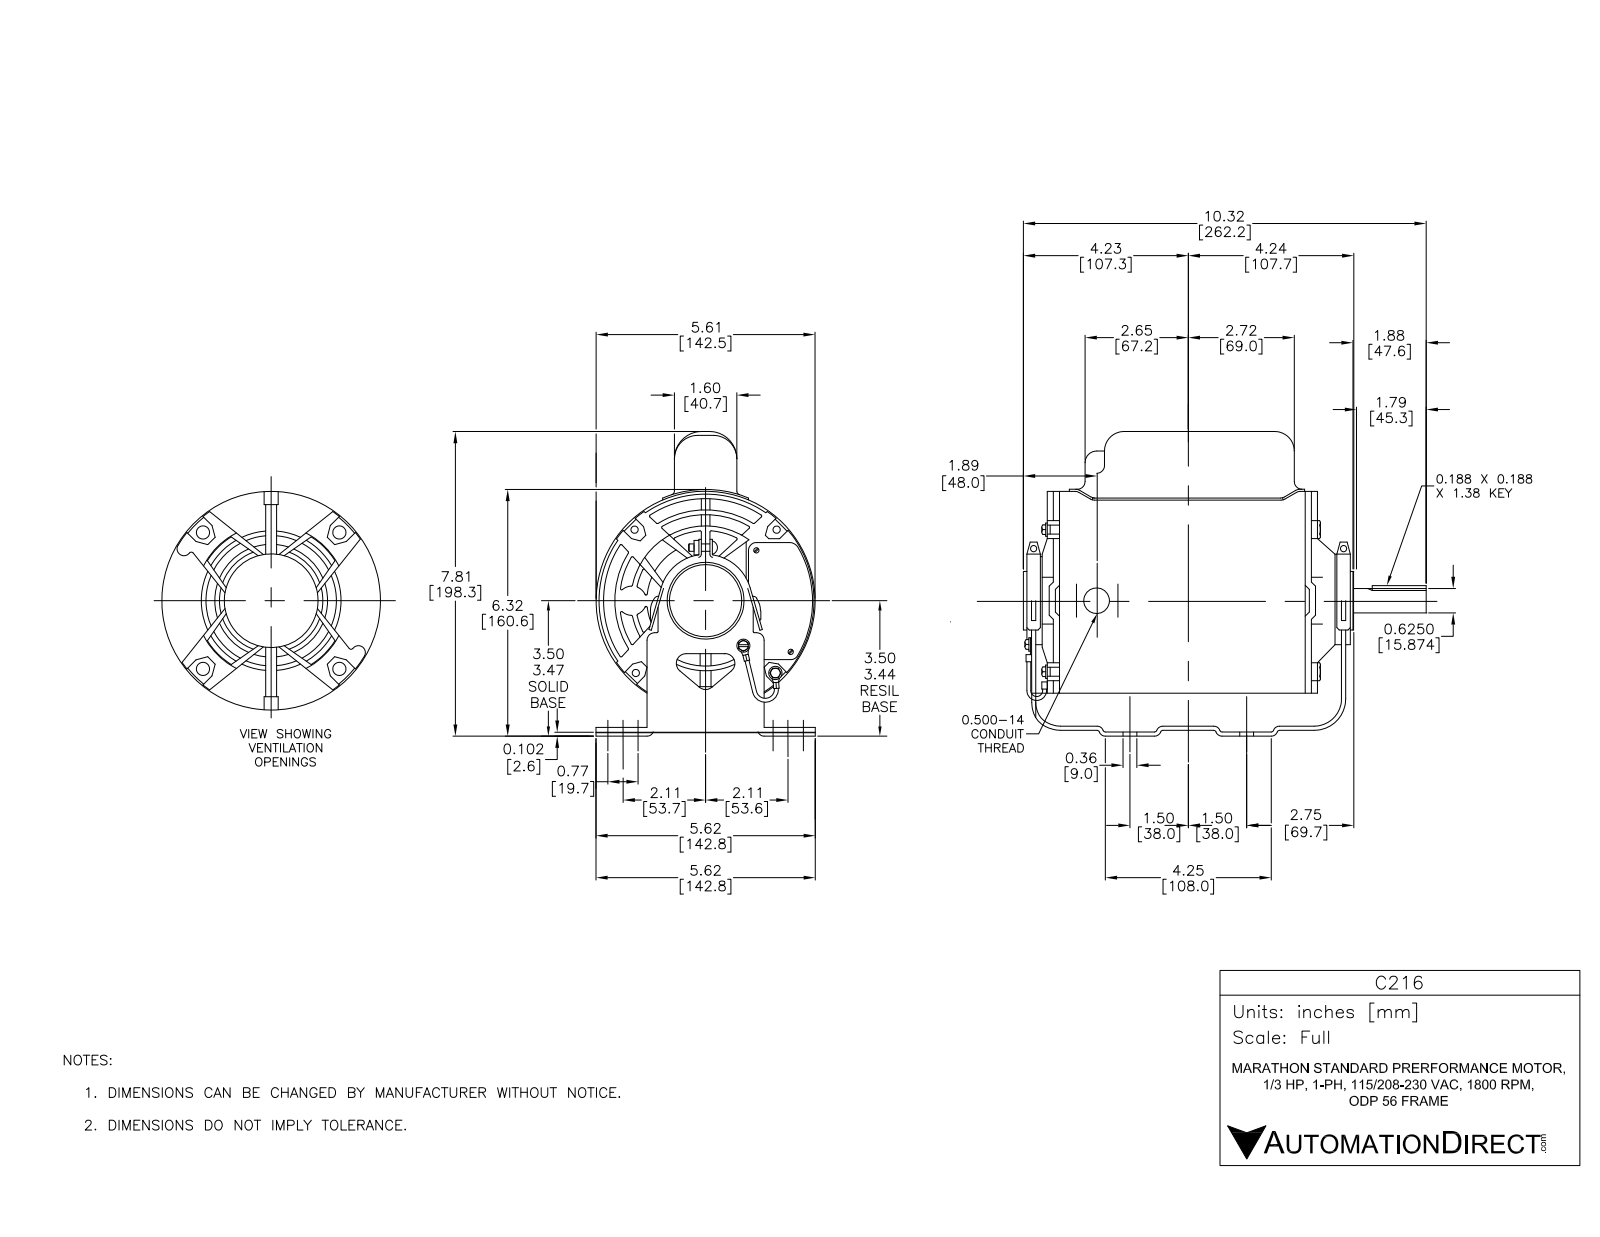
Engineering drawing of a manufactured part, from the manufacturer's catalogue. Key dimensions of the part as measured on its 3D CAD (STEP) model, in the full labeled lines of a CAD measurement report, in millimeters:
Part name (STEP PRODUCT): 52A101468P2
STEP written by: SolidWorks 2015 (CONFIG_CONTROL_DESIGN)
Units: millimetres
Bodies: 0 solids, 2325 faces (609 planar, 674 cylindrical, 1042 other)
Overall size (bounding box): 263.6 × 210.2 × 165.1
Round holes (diameter × count): ⌀6.4 ×7, ⌀5.5 ×4, ⌀5.6 ×4, ⌀3.9 ×2, ⌀4.4 ×2, ⌀5.1 ×2, ⌀12.7 ×2, ⌀3.7 ×1, ⌀5.3 ×1, ⌀17.4 ×1, ⌀19 ×1, ⌀32 ×1
Round bosses / shafts (diameter × count): ⌀4.8 ×7, ⌀10.1 ×6, ⌀8.8 ×2, ⌀8.5 ×2, ⌀142.8 ×1, ⌀142.3 ×1, ⌀63.5 ×1, ⌀62 ×1
Partial cylindrical surfaces — rounded edges, fillets, slot ends (radius × count): R0.5 ×48, R1.5 ×47, R4.7 ×46, R0.8 ×37, R2.3 ×34, R6.4 ×34, R8.7 ×12, R4.4 ×8
Main face-to-face distances: 2.3, 2.1, 4.4, 0.8, 2.9, 182.1, 1, 13, 195.1, 2.3
Hole centre spacings: 65.1, 83.8, 92, 16.3, 30.2, 61, 65.5, 65.9
